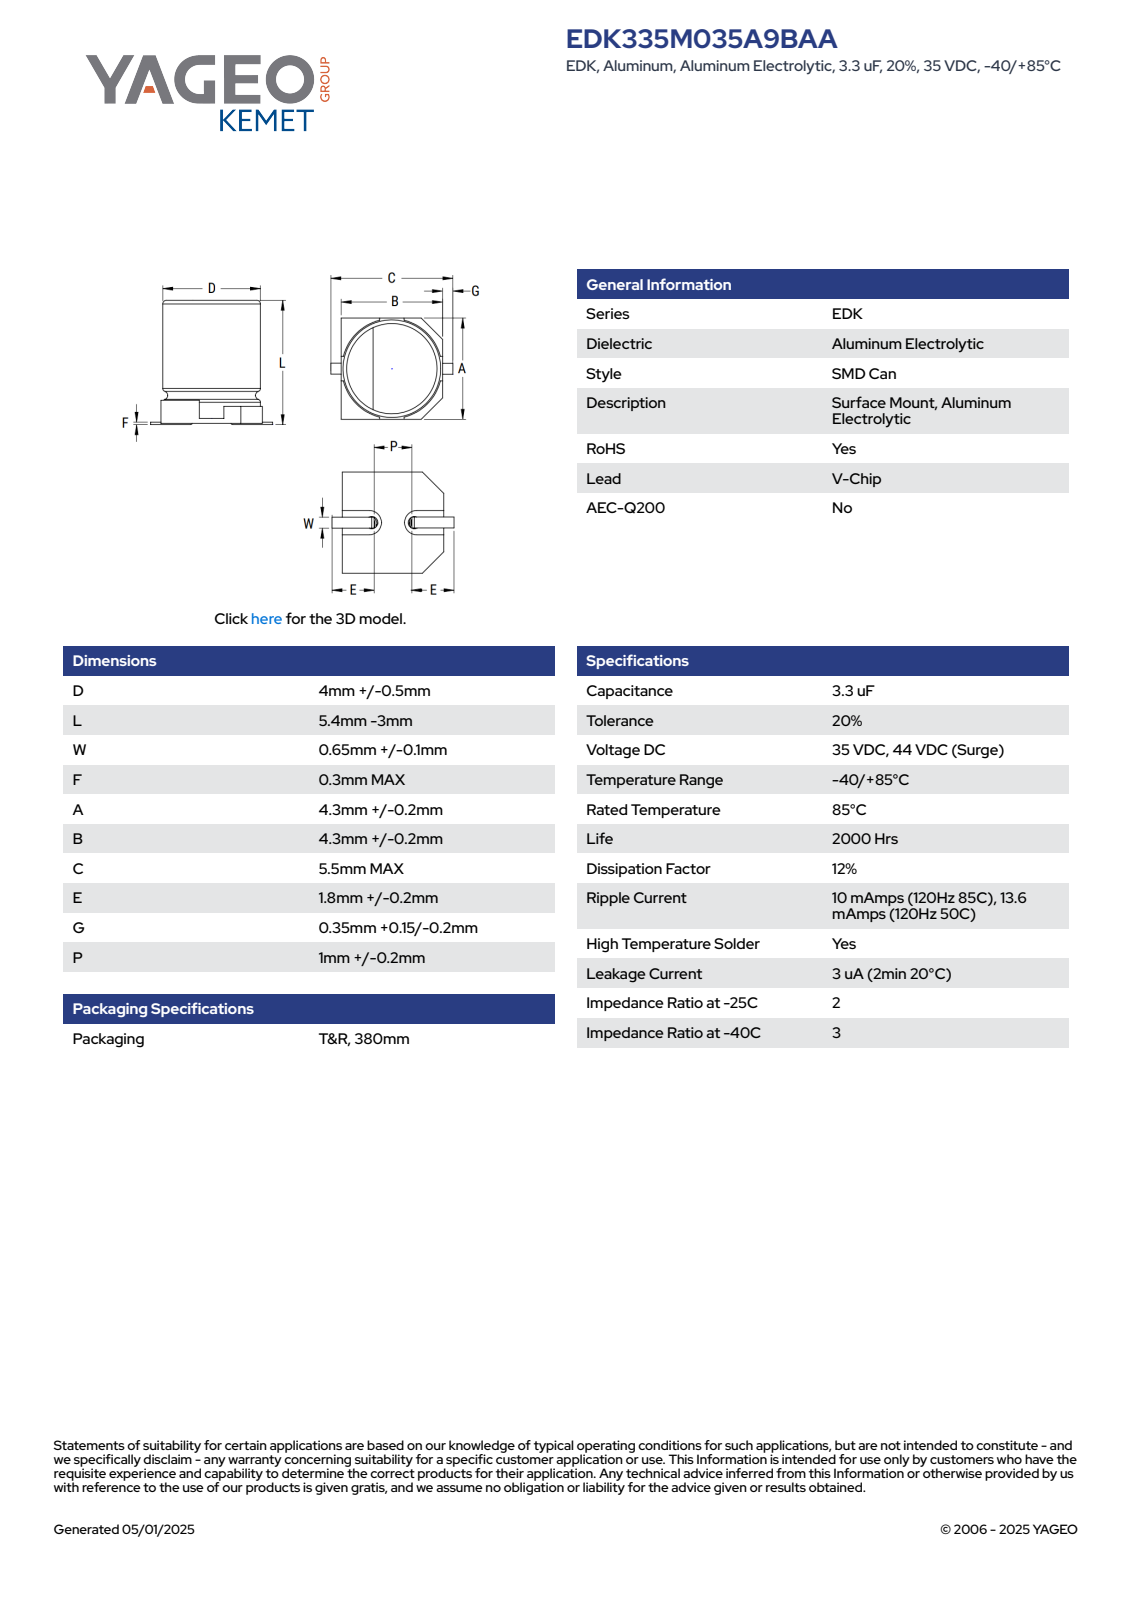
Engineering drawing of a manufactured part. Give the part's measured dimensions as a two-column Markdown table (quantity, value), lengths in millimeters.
| quantity | value |
| --- | --- |
| part name | CAC_S_4X5.4_D4.5L5.65W0.75F0.3A4.5B4.5C5.5E2P1.2 |
| STEP written by | SolidWorks 2014 (AUTOMOTIVE_DESIGN) |
| units | millimeters |
| bodies | 5 solids, 78 faces (61 planar, 11 cylindrical, 6 other) |
| overall size | 5.66 × 5.2 × 4.5 |
| volume | 81 mm³ |
| surface area | 161 mm² |
| round bosses / shafts (diameter × count) | 4.3 × 1 |
| partial cylindrical surfaces (radius × count) | 0.2 × 2, 1.79 × 1, 2.25 × 1 |
| main face-to-face distances | 5.35, 5.07, 5.36, 5.08, 1.13, 4.5, 0.58, 5.65, 5.66, 3.37 |
